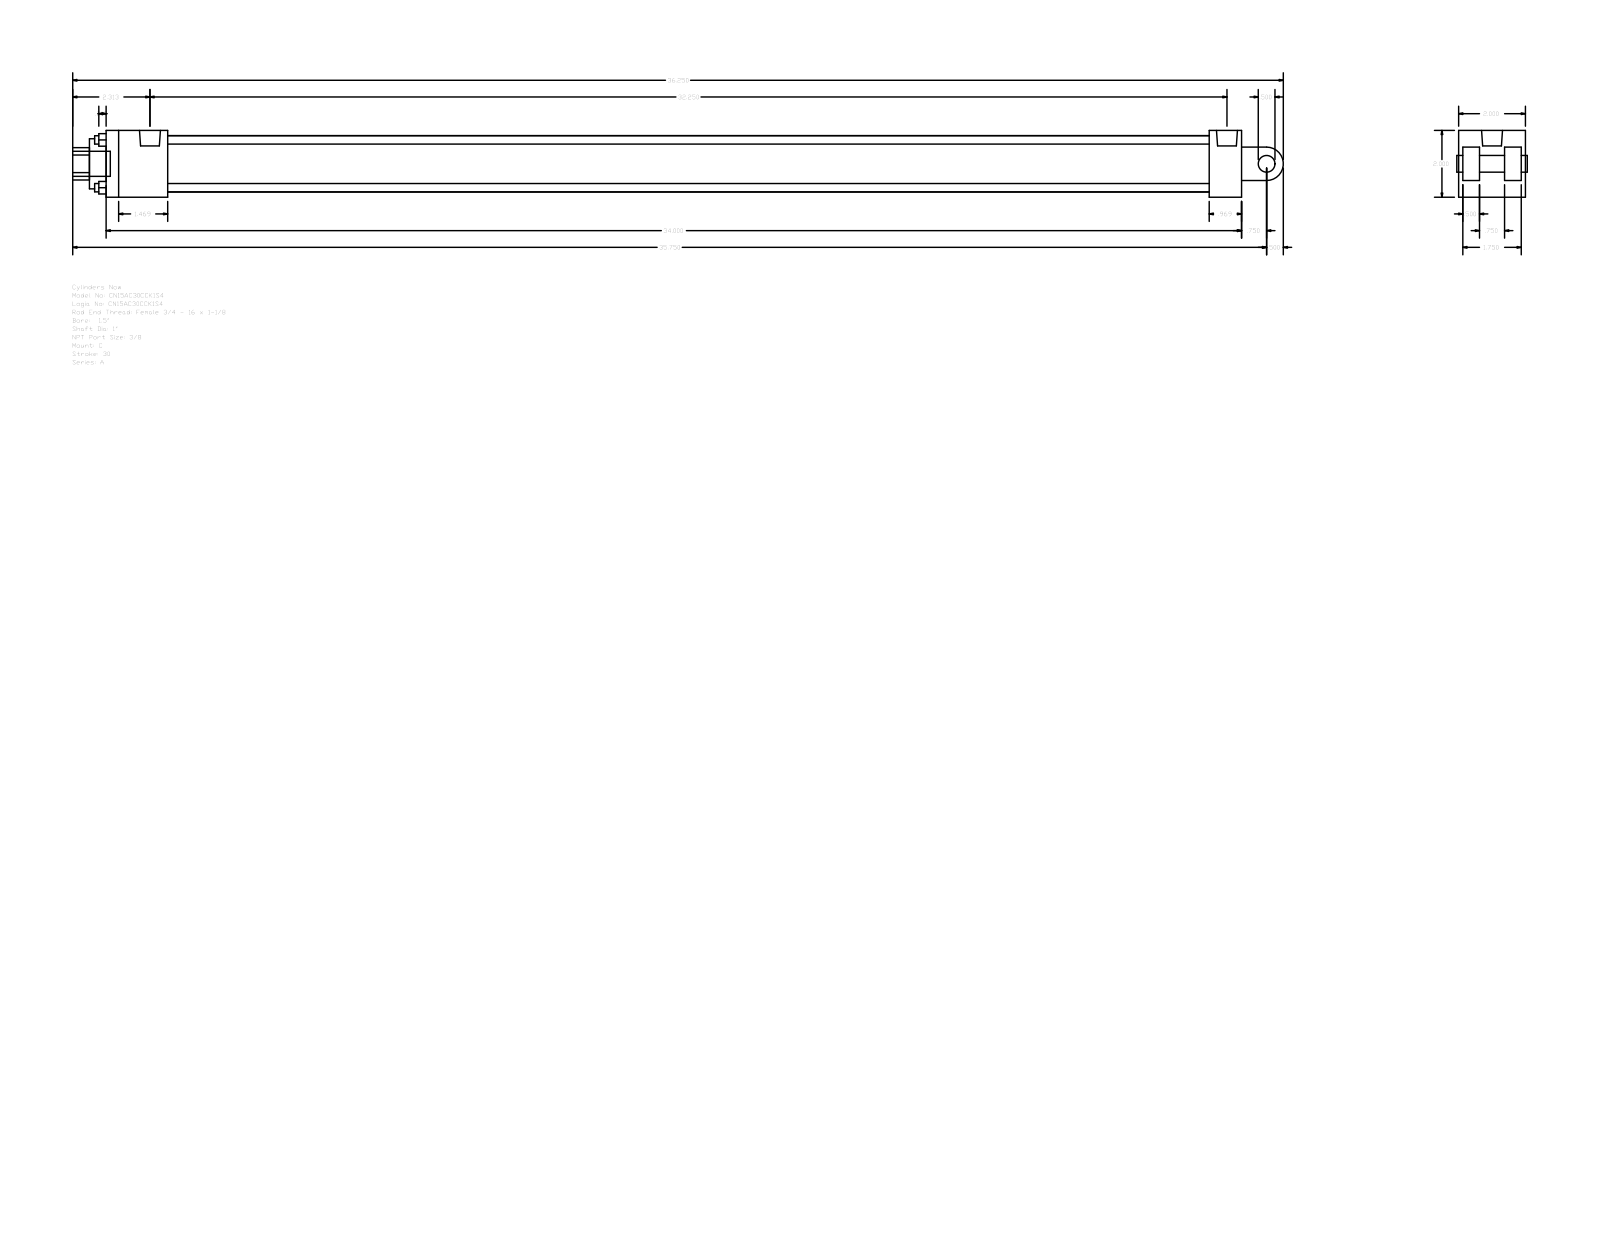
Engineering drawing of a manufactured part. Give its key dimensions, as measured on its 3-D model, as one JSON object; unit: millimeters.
{"part_name": "A_C__0150_1", "step_written_by": "GSSL Pune (CONFIG_CONTROL_DESIGN)", "units": "millimeters", "bodies": {"solids": 0, "faces": 99, "planar": 70, "cylindrical": 29, "other": 0}, "overall_size": [920.75, 50.8, 50.8], "round_holes": [[6.35, 4], [5.56, 2], [15.93, 1], [25.4, 1], [38.1, 1], [42.93, 1]], "round_bosses_or_shafts": [[5.56, 2], [19.05, 1], [15.93, 1], [12.7, 1]], "partial_cylinders_radius": [[12.29, 1], [12.7, 1]], "face_to_face_distances": [50.8, 12.7, 3.17, 15.87, 47.63, 34.93, 31.76, 863.6, 838.99, 24.61], "hole_center_spacings": [25.68, 36.32, 51.36, 3.97]}
